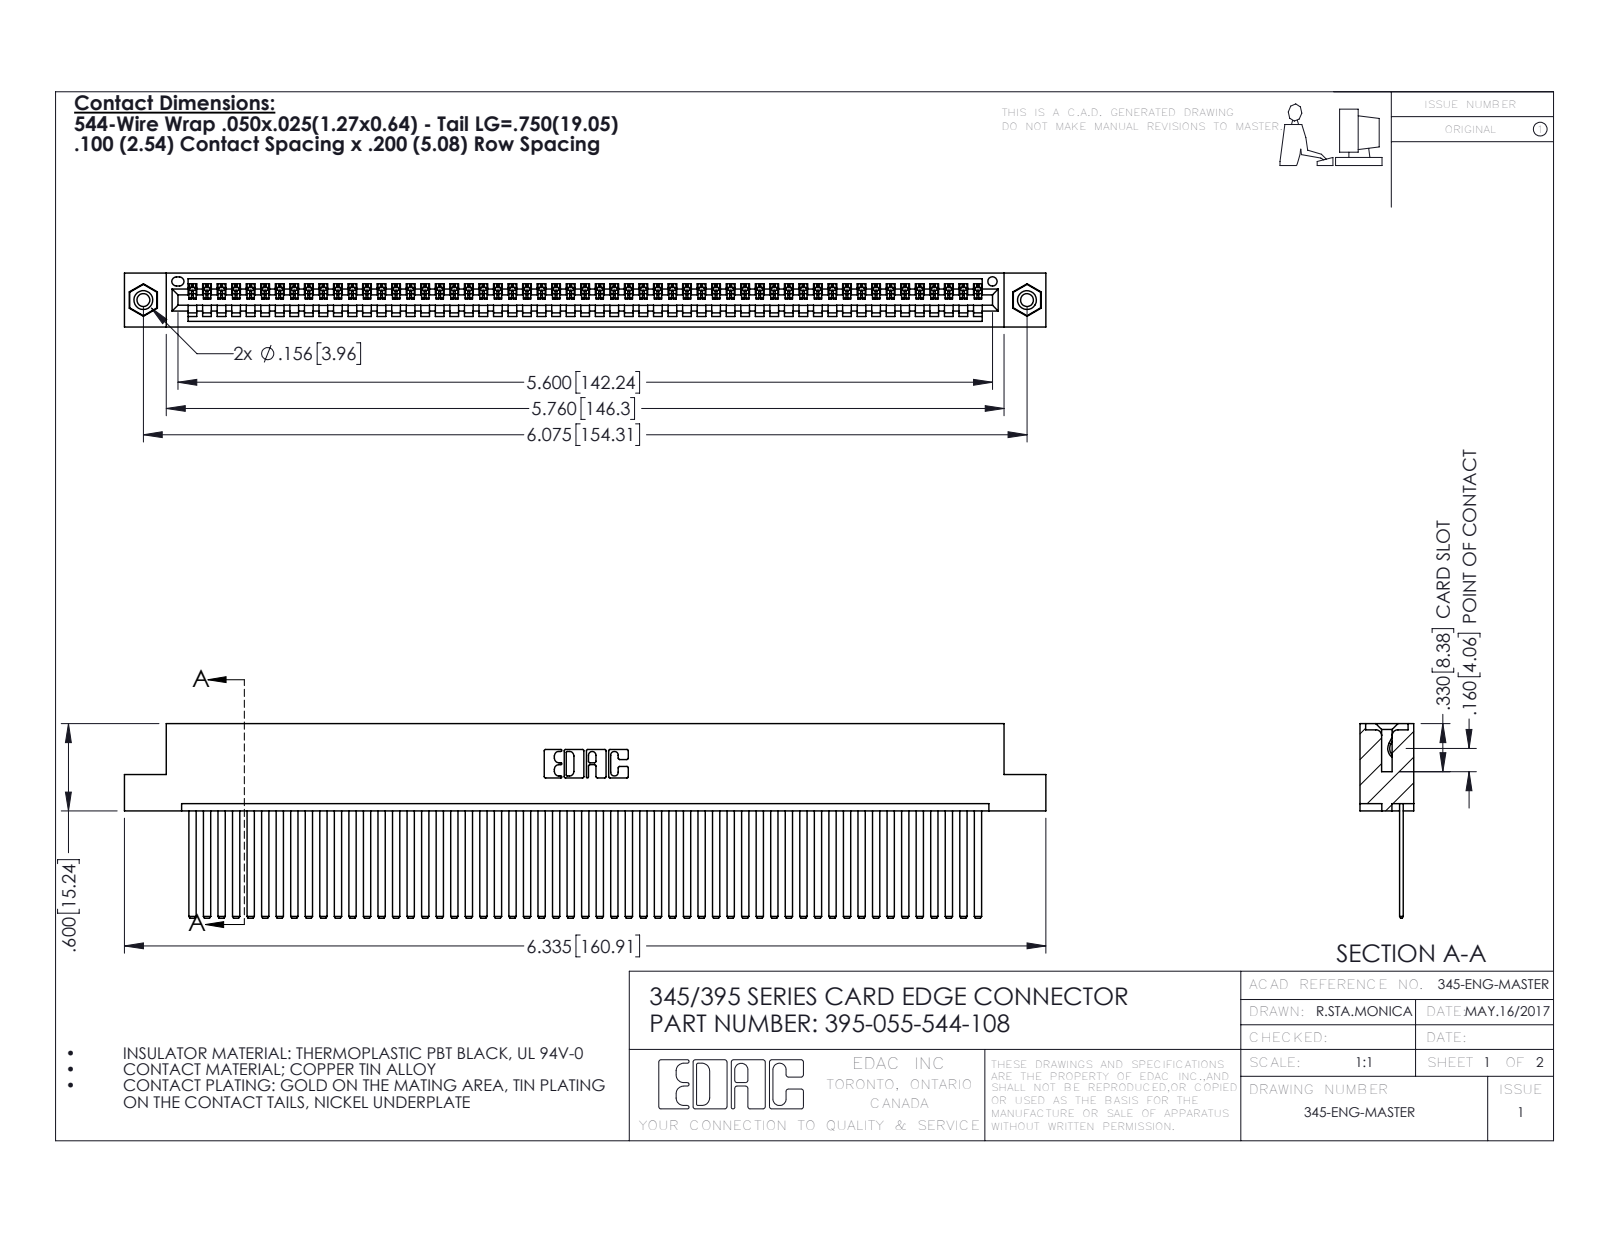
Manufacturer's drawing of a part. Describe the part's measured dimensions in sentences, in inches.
The part is named "345 Part_Flush Mounting Lugs - 0.156 Dia-TI; 345-250-001_345-250-003-102; 345-292-001_345-293-144; 395-055-544-108". Its 3-D file was written by "SolidWorks 2016 (CONFIG_CONTROL_DESIGN)". It is 58 solids with 3046 faces: 2092 planar, 938 cylindrical and 16 other. Overall it measures 6.335 by 1.337 by 0.37 inches. Its volume is 0.978 cubic inches and its surface area 36.27 square inches. Round holes: 2 of diameter 0.089, 2 of diameter 0.125, 2 of diameter 0.156, 1 of diameter 0.064. Round bosses or shafts: 2 of diameter 0.155. Partial cylindrical surfaces (rounded edges, fillets, slot ends): 110 of radius 0.006, 22 of radius 0.01, 6 of radius 0.007, 6 of radius 0.031, 3 of radius 0.026, 2 of radius 0.031, 2 of radius 0.04, 1 of radius 0.014. The main face-to-face distances are 0.072, 0.298, 0.025, 0.098, 0.272, 0.37, 0.2, 0.225, 0.149, 0.072. The hole center spacings are 0.27, 5.839, 6.075.
